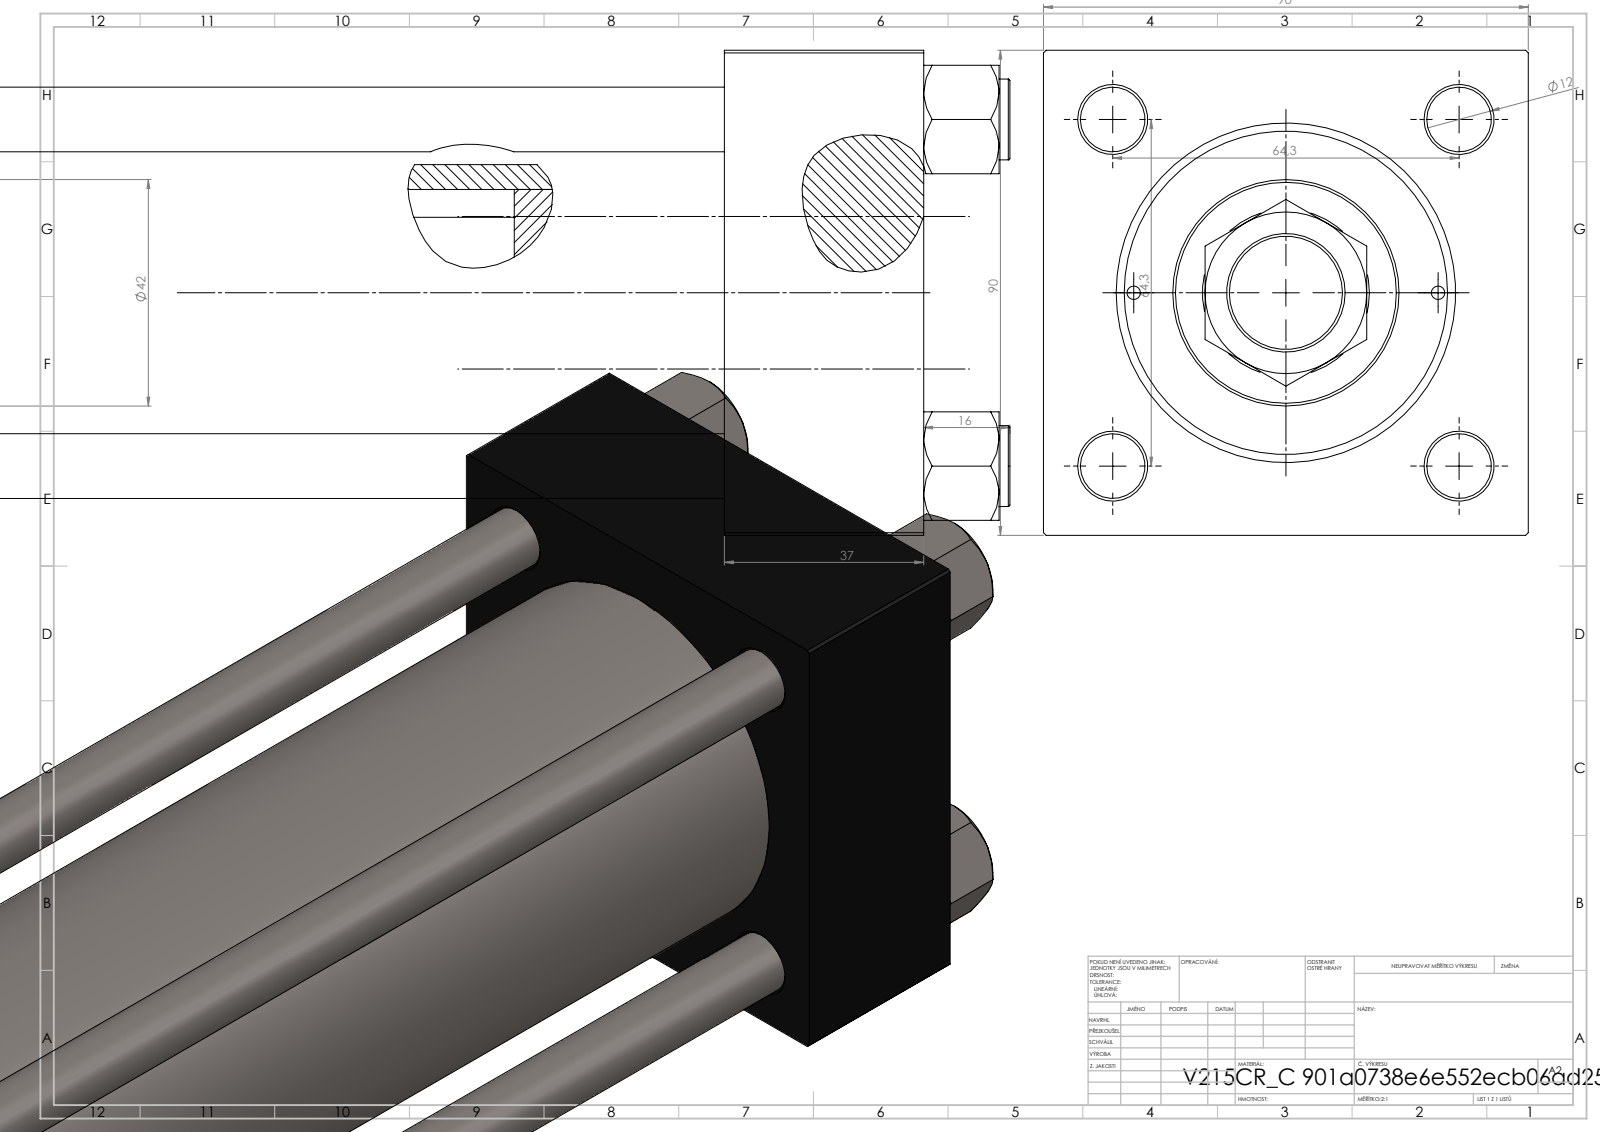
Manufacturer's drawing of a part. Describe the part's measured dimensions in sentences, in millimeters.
The part is named "NUT_M5_C; V215CR_C_Body; MFA; V215CR_VCP_C (+2 more)". Its 3-D file was written by "SolidWorks 2019 (CONFIG_CONTROL_DESIGN)". It is 12 solids with 1206 faces: 544 planar, 94 cylindrical and 568 other. Overall it measures 578 by 90 by 90 millimeters. Its volume is 1 529 000 cubic millimeters and its surface area 400 436 square millimeters. Round holes: 4 of diameter 12, 2 of diameter 2.5, 2 of diameter 7, 2 of diameter 20.96, 2 of diameter 30, 1 of diameter 18.5, 1 of diameter 28, 1 of diameter 31, 1 of diameter 50, 1 of diameter 60, 1 of diameter 63. Round bosses or shafts: 4 of diameter 15, 1 of diameter 69, 1 of diameter 42, 1 of diameter 22, 1 of diameter 14. Partial cylindrical surfaces (rounded edges, fillets, slot ends): 1 of radius 13.5. The main face-to-face distances are 90, 37, 485, 448, 426, 389, 59, 456.3, 419.3, 30.3. The hole center spacings are 32.39, 45.47, 64.3, 68.42, 28.25, 90.93, 56.5, 427.5.
